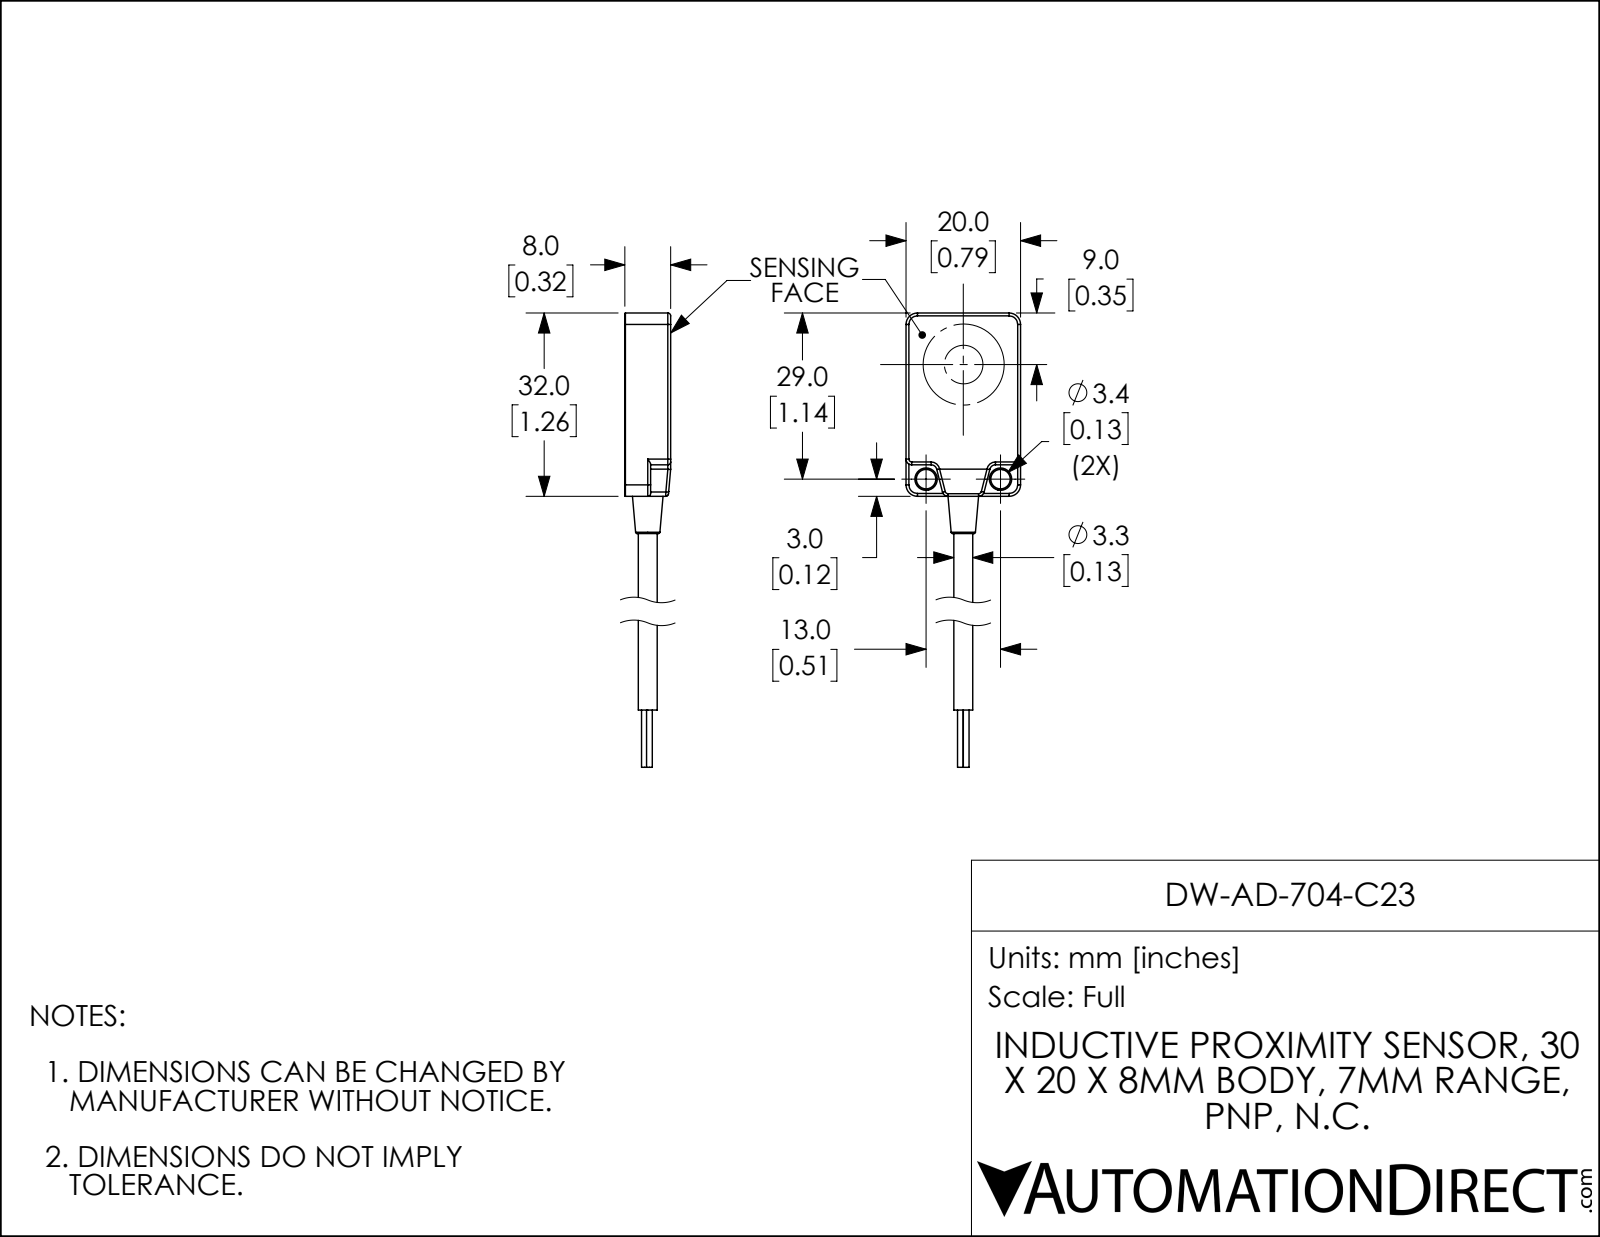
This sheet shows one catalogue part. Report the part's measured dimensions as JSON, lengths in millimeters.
{"part_name": "DW-AD-703-C23", "step_written_by": "SolidWorks 2017 (AUTOMOTIVE_DESIGN)", "units": "millimeters", "bodies": {"solids": 1, "faces": 97, "planar": 37, "cylindrical": 36, "other": 24}, "overall_size": [133, 20, 8], "volume_mm3": 5640, "surface_area_mm2": 3203, "round_holes": [[3.4, 2]], "round_bosses_or_shafts": [[1, 3], [3.3, 1]], "partial_cylinders_radius": [[0.5, 10], [1, 6], [0.5, 4], [0.6, 4], [2, 4]], "face_to_face_distances": [8, 20, 32, 4.5, 3.5, 26.5, 5.5, 0.9, 1, 18.1], "hole_center_spacings": [13]}
